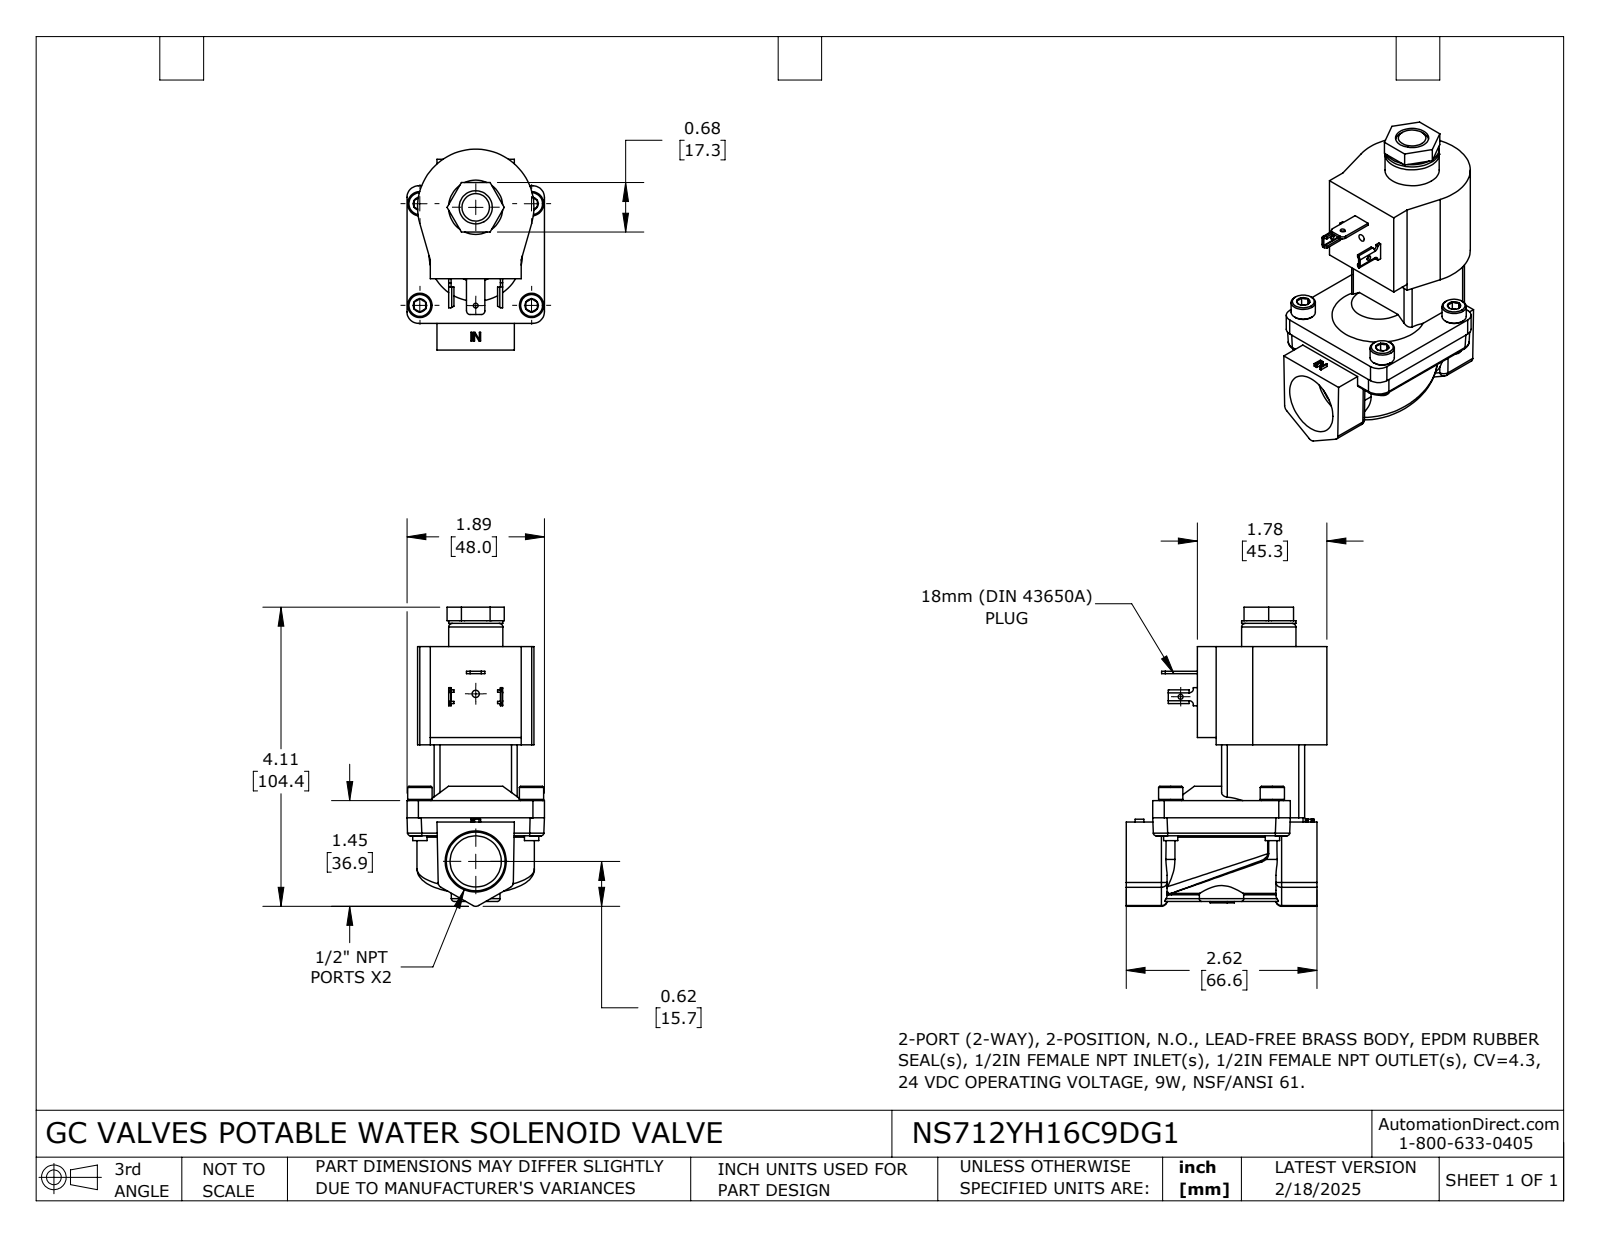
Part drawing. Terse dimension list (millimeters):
name: NS712YH16C9DG1
written by: SolidWorks 2024 (CONFIG_CONTROL_DESIGN)
unit: mm
bodies: 2 solids, 501 faces (276 planar, 118 cylindrical, 107 other)
size: 104.4 × 70.12 × 48
volume: 130 218 mm³; area: 30 112 mm²
holes: 1× ⌀1.68, 1× ⌀1.7, 1× ⌀2.53, 1× ⌀11.58, 1× ⌀17.86, 1× ⌀30.48
bosses: 4× ⌀8.5, 4× ⌀5, 1× ⌀18.95
rounds: 15× R2, 6× R0.5, 6× R1, 4× R0.15, 4× R1.04, 4× R4, 4× R5, 2× R1.27
face distances: 53.79, 29, 19.5, 34.29, 33.3, 37.44, 9.5, 27, 38.5, 12.3
hole spacings: 34.29, 58.5
